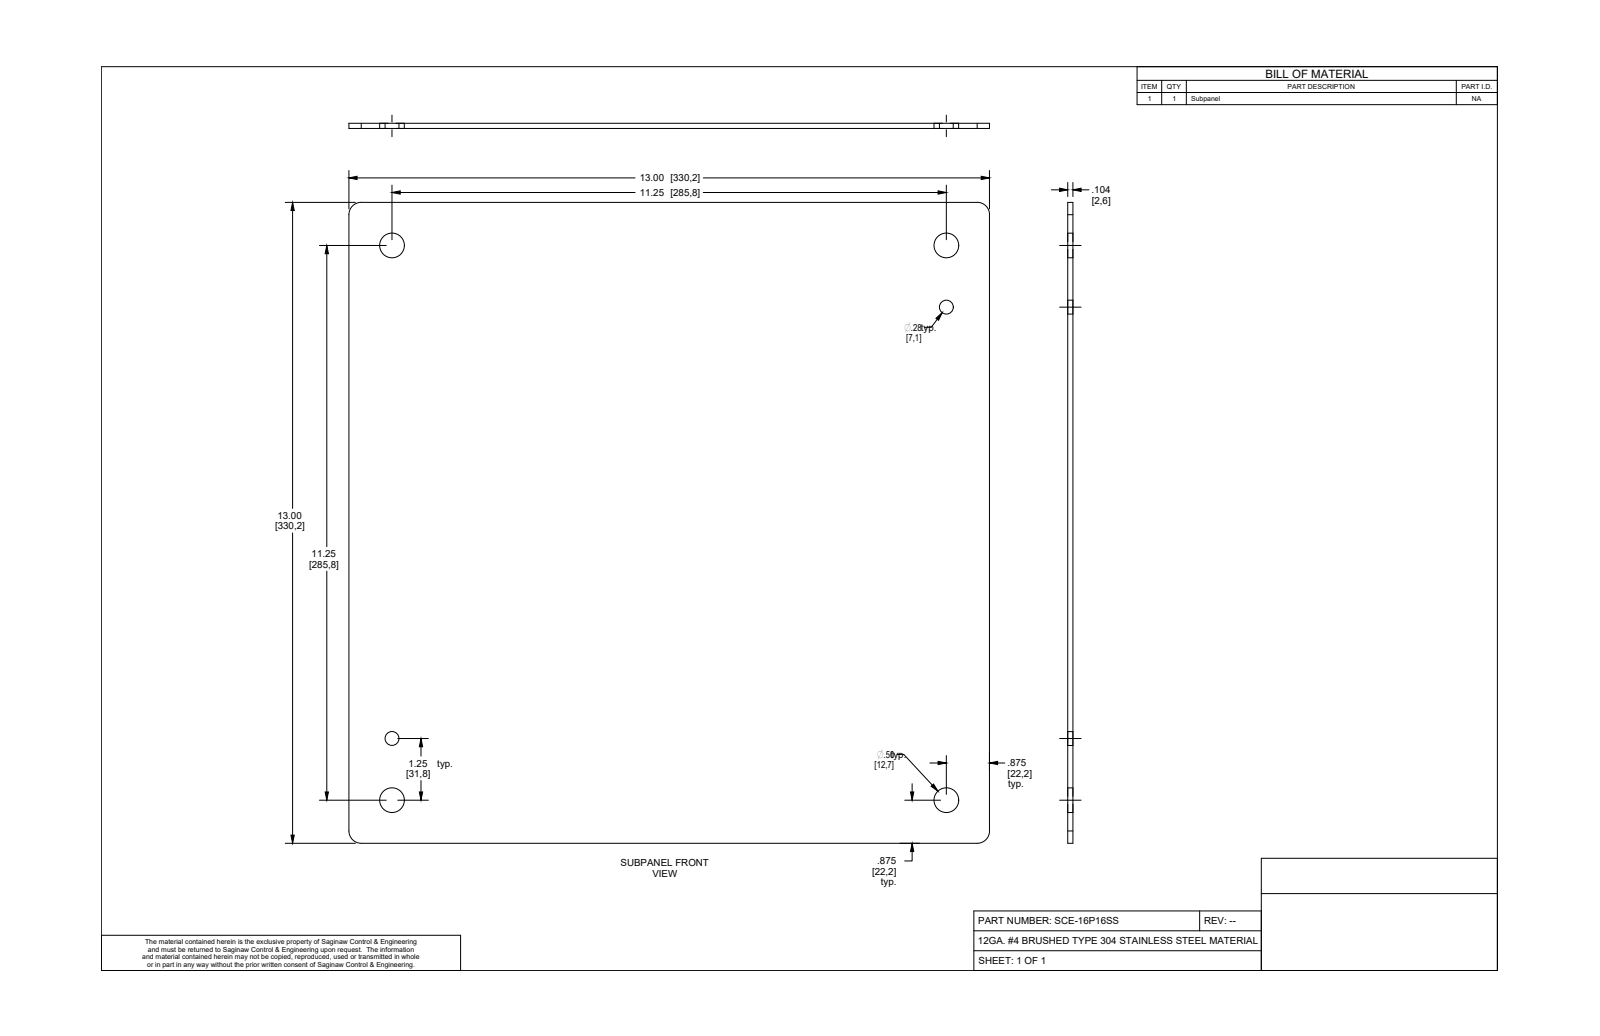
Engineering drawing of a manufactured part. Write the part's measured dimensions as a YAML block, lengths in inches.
part_name: "SCE-16P16SS"
step_written_by: "SolidWorks 2019 (CONFIG_CONTROL_DESIGN)"
units: inches
bodies: {solids: 1, faces: 16, planar: 6, cylindrical: 10, other: 0}
overall_size: [13, 13, 0.104]
volume: 17.48
surface_area: 342.3
round_holes:
  - {diameter: 0.5, count: 4}
  - {diameter: 0.281, count: 2}
partial_cylinders:
  - {radius: 0.25, count: 4}
face_to_face_distances: [0.104, 13]
hole_center_spacings: [11.25, 1.25, 10, 11.32, 15.052, 15.911, 14.252]
